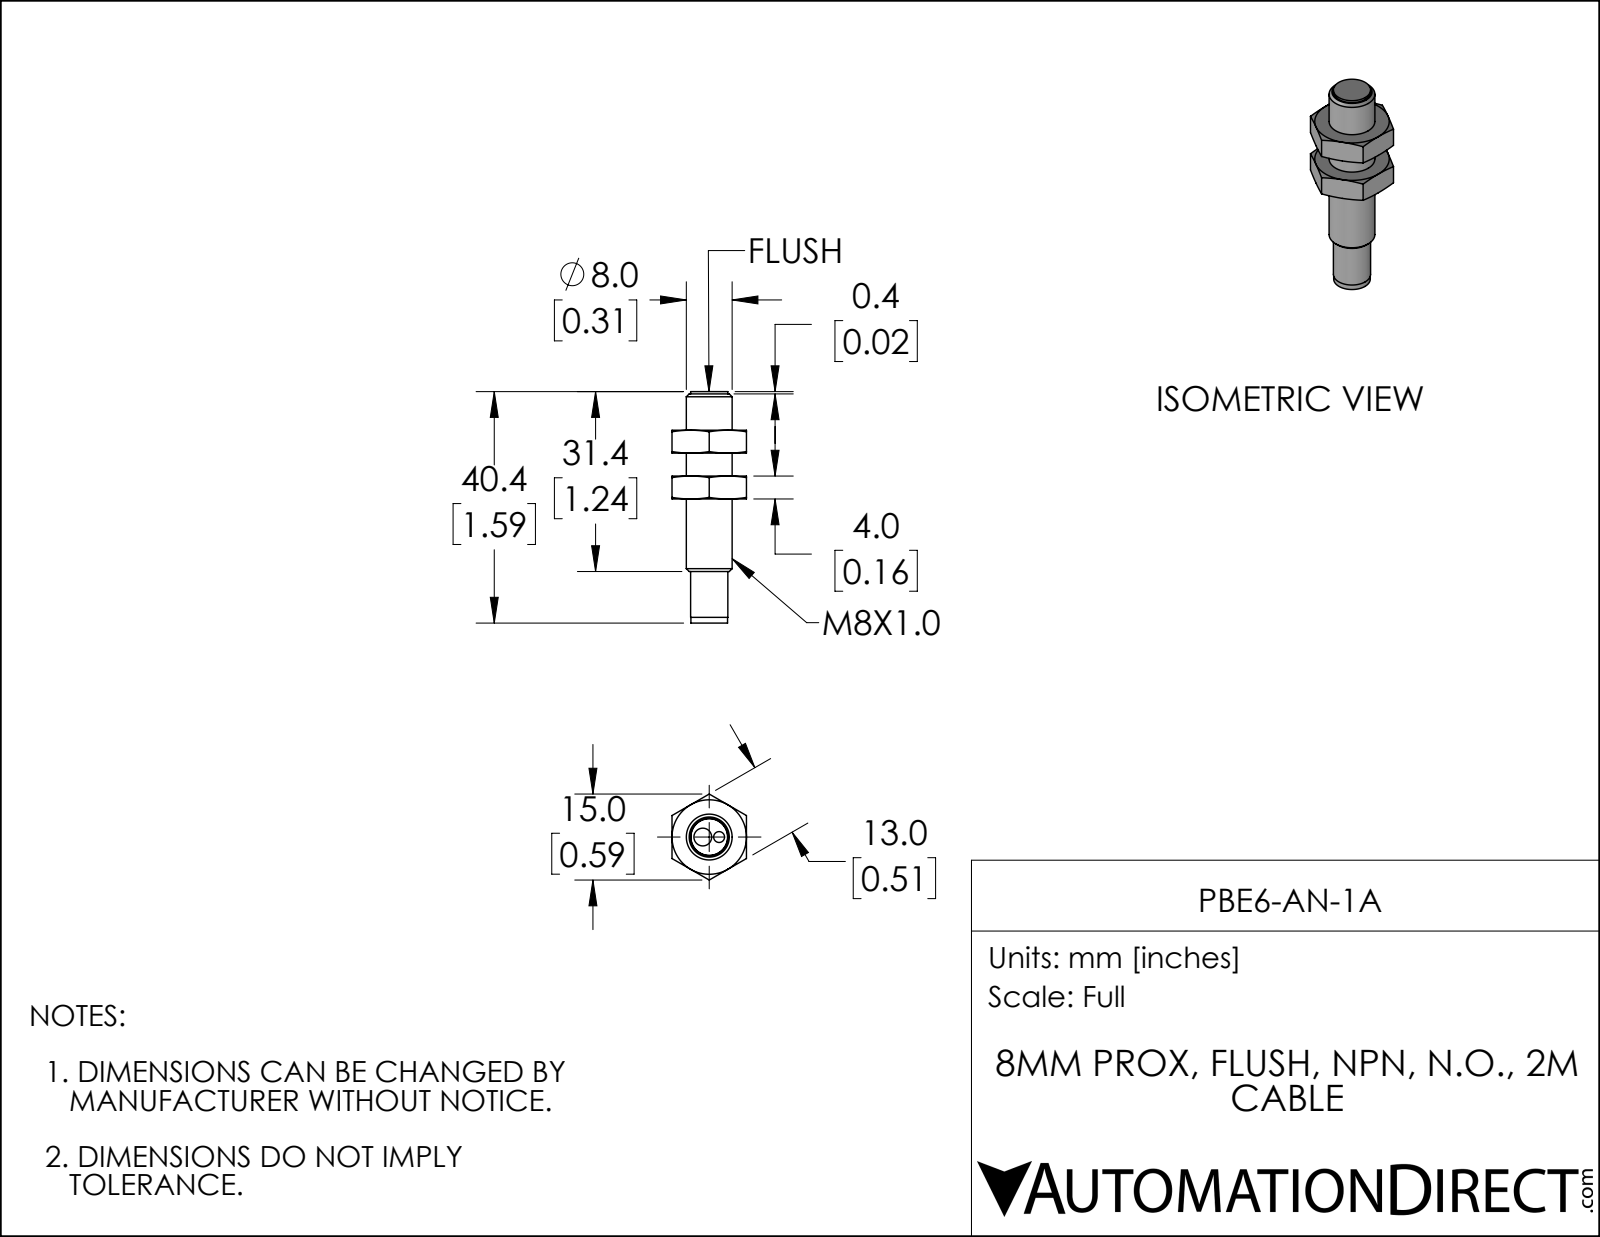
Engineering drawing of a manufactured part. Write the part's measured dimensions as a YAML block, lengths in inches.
part_name: "DSD-0261"
step_written_by: "SolidWorks 2019 (AUTOMOTIVE_DESIGN)"
units: inches
bodies: {solids: 1, faces: 15, planar: 7, cylindrical: 6, other: 2}
overall_size: [1.591, 0.315, 0.315]
volume: 0.113
surface_area: 1.661
round_holes:
  - {diameter: 0.075, count: 1}
  - {diameter: 0.122, count: 1}
round_bosses_or_shafts:
  - {diameter: 0.315, count: 1}
  - {diameter: 0.256, count: 1}
  - {diameter: 0.252, count: 1}
face_to_face_distances: [1.591, 1.551, 0.039, 0.016, 1.535, 1.575, 1.236, 1.22, 0.315, 0.354]
hole_center_spacings: [0.112]
